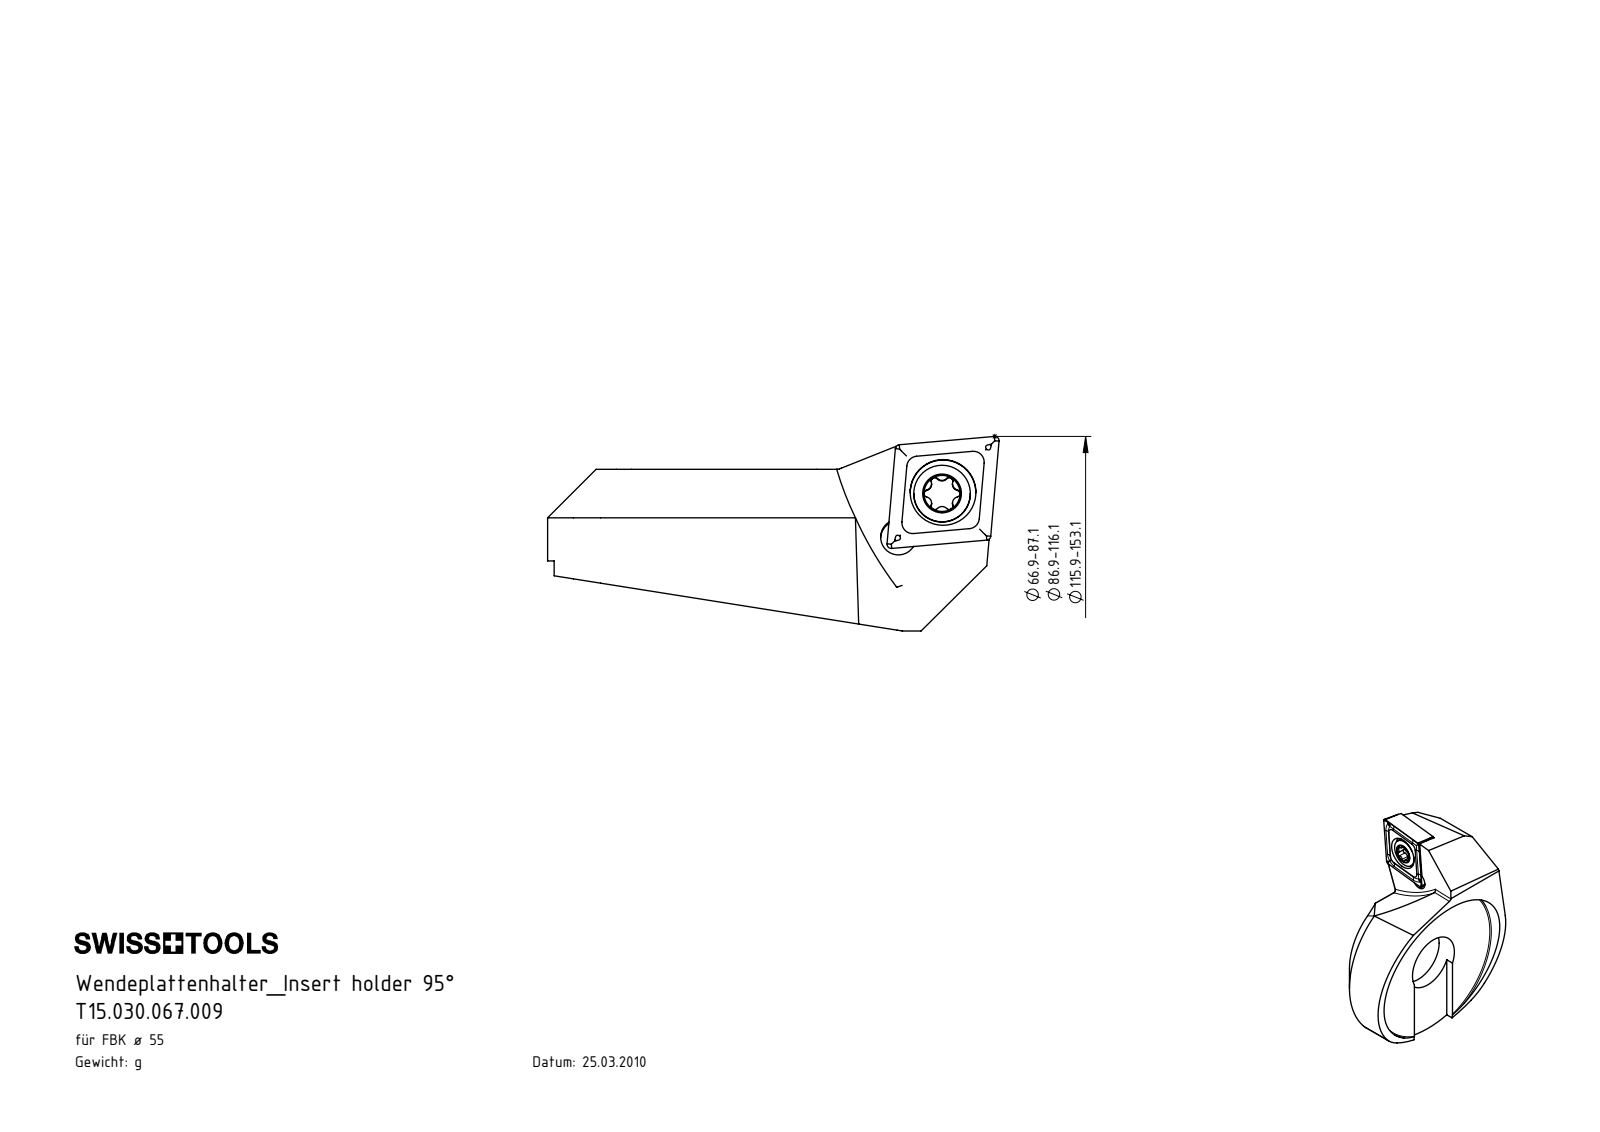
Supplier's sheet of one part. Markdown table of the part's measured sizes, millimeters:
| quantity | value |
| --- | --- |
| part name | CCMT09T304; F55.WCB.002.013; WCB-ER2.001.009_A; F55-WCB.002.013_D_fertigbearbeitet |
| STEP written by | SolidWorks 2017 (AUTOMOTIVE_DESIGN) |
| units | millimeters |
| bodies | 5 solids, 128 faces (50 planar, 31 cylindrical, 47 other) |
| overall size | 41.9 × 33.1 × 18.05 |
| volume | 8 191 mm³ |
| surface area | 5 040 mm² |
| round holes (diameter × count) | 3.3 × 2, 4.4 × 1, 6.1 × 1, 11 × 1, 17 × 1, 30 × 1 |
| round bosses / shafts (diameter × count) | 5.25 × 1, 4 × 1 |
| partial cylindrical surfaces (radius × count) | 0.34 × 6, 0.59 × 6, 0.5 × 2, 10 × 2, 1.65 × 1, 16.55 × 1, 20.9 × 1, 30 × 1 |
| main face-to-face distances | 10, 9, 1, 3.77, 5, 6, 4, 8.5, 7.5, 2.5 |
| hole center spacings | 5.73, 5.86 |
